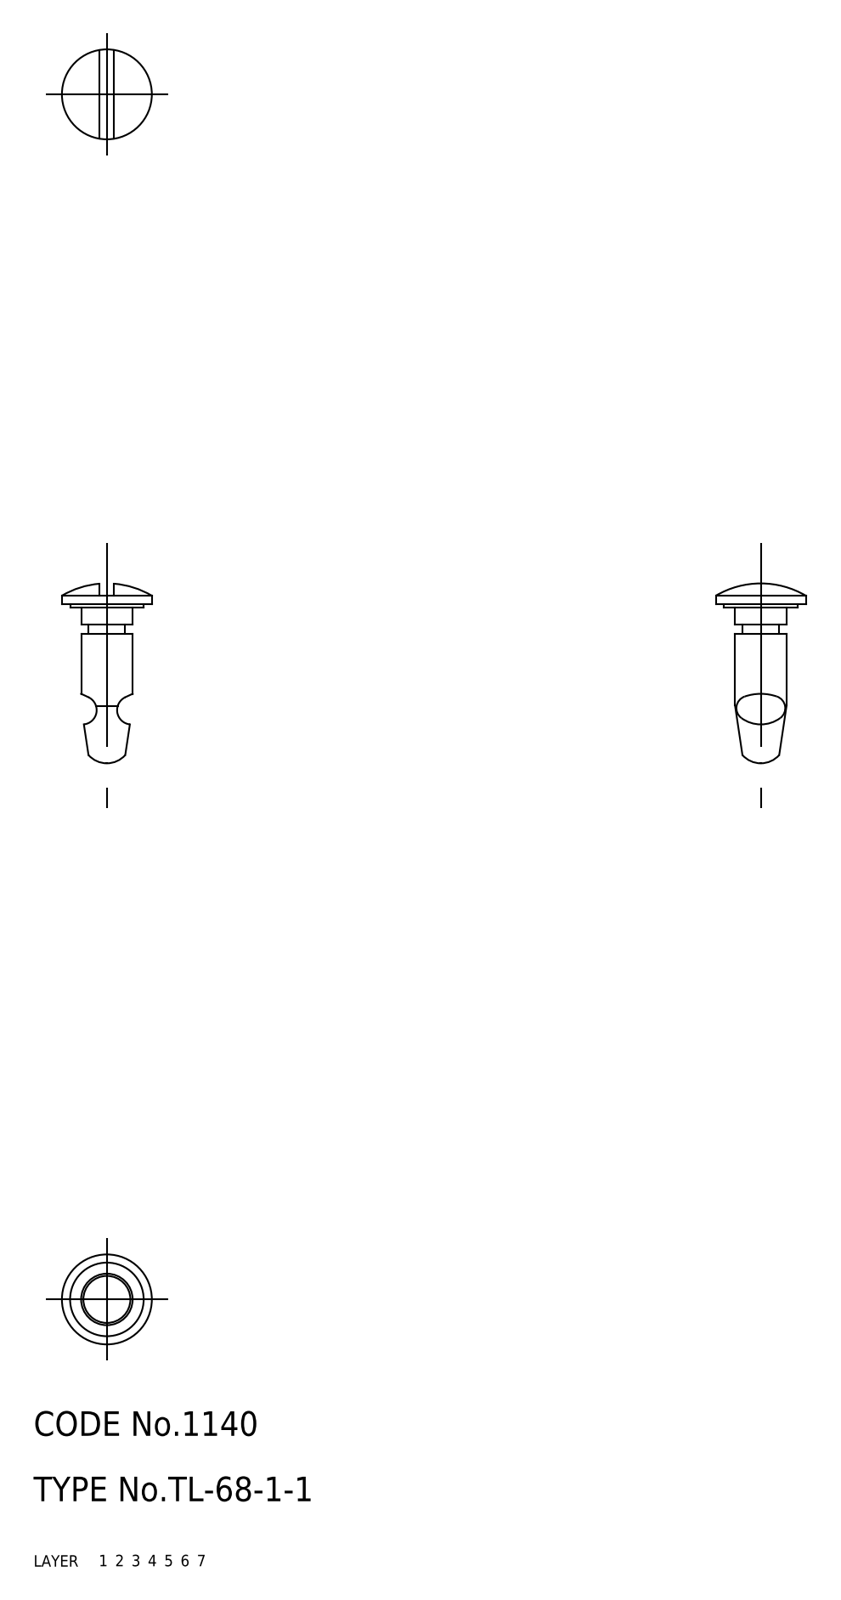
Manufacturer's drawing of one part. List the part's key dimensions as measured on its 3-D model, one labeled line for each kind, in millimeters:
Part name (STEP PRODUCT): fastener
STEP written by: CADfix (AUTOMOTIVE_DESIGN)
Units: millimetres
Bodies: 1 solid, 26 faces (0 planar, 0 cylindrical, 26 other)
Overall size (bounding box): 21.96 × 11 × 11
Volume: 647 mm³ · Surface area: 624 mm²
